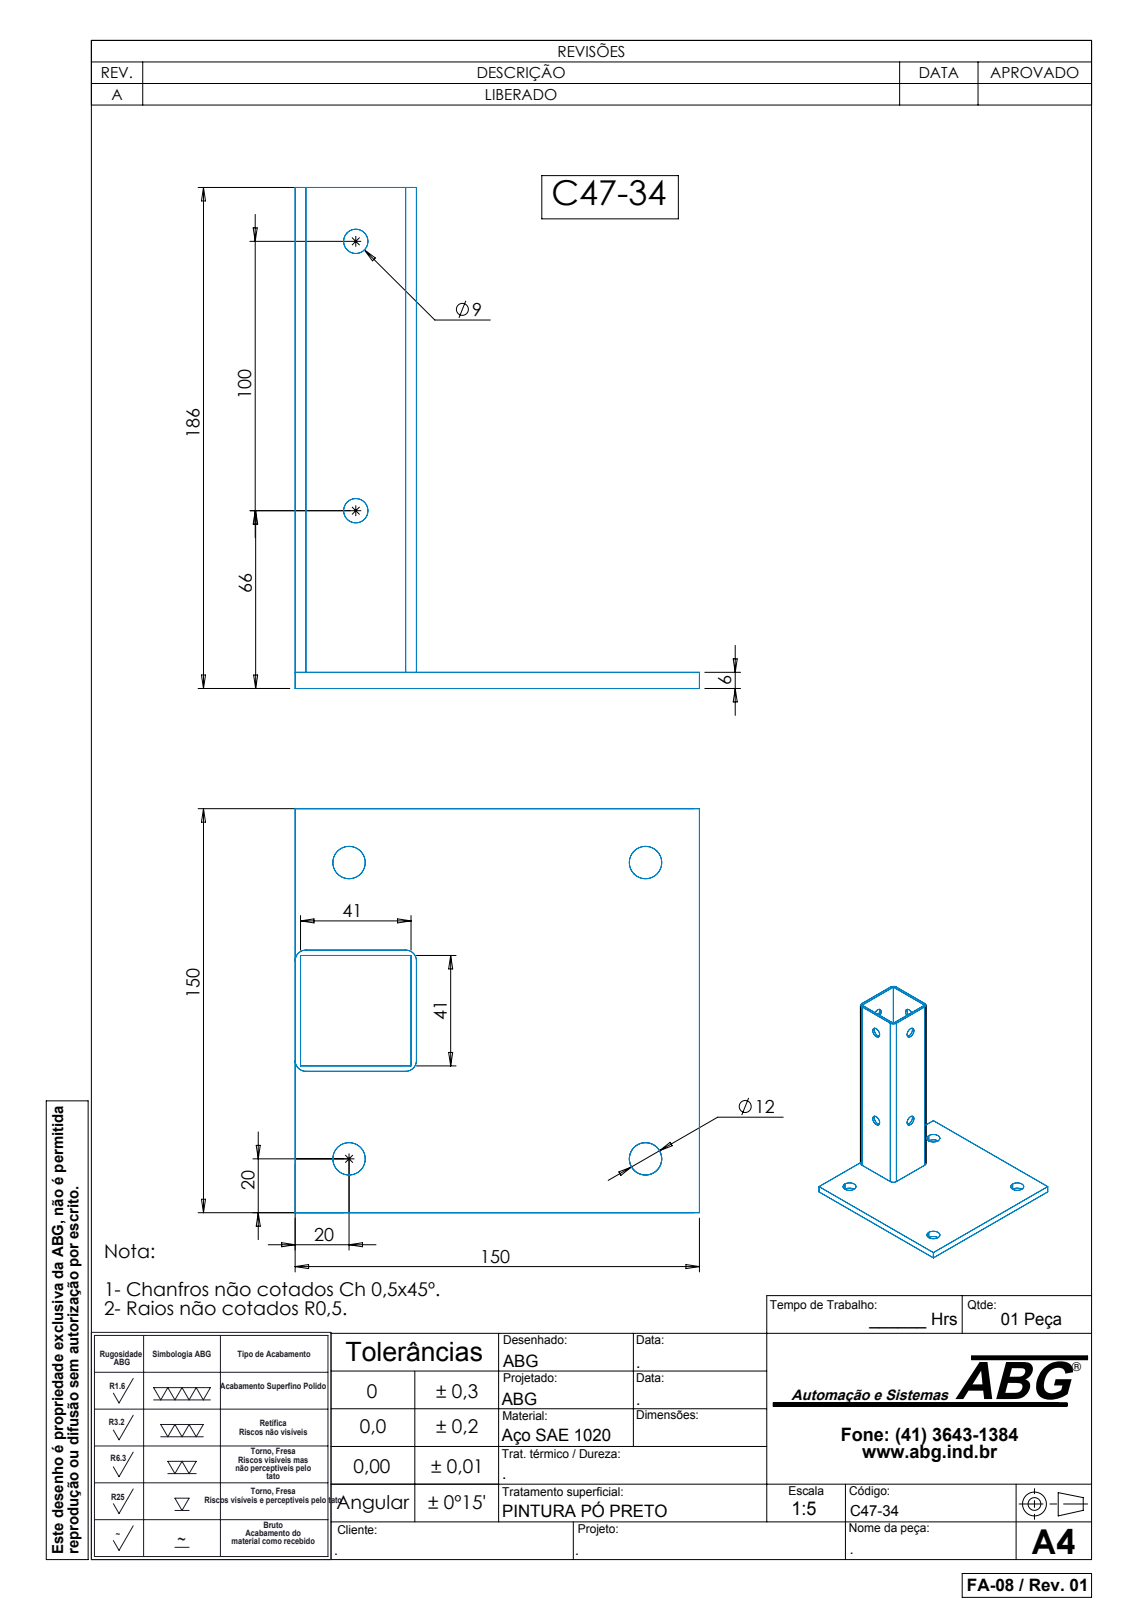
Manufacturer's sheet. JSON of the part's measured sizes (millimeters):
{"part_name": "C47-34", "step_written_by": "SolidWorks 2007 (CONFIG_CONTROL_DESIGN)", "units": "millimeters", "bodies": {"solids": 1, "faces": 43, "planar": 15, "cylindrical": 28, "other": 0}, "overall_size": [186, 150, 150], "volume_mm3": 190716, "surface_area_mm2": 108718, "round_holes": [[9, 4], [12, 4]], "partial_cylinders_radius": [[4, 4]], "face_to_face_distances": [43, 2, 6, 41, 45, 150, 52.5, 54.5, 95.5, 97.5], "hole_center_spacings": [110, 100, 155.56]}
